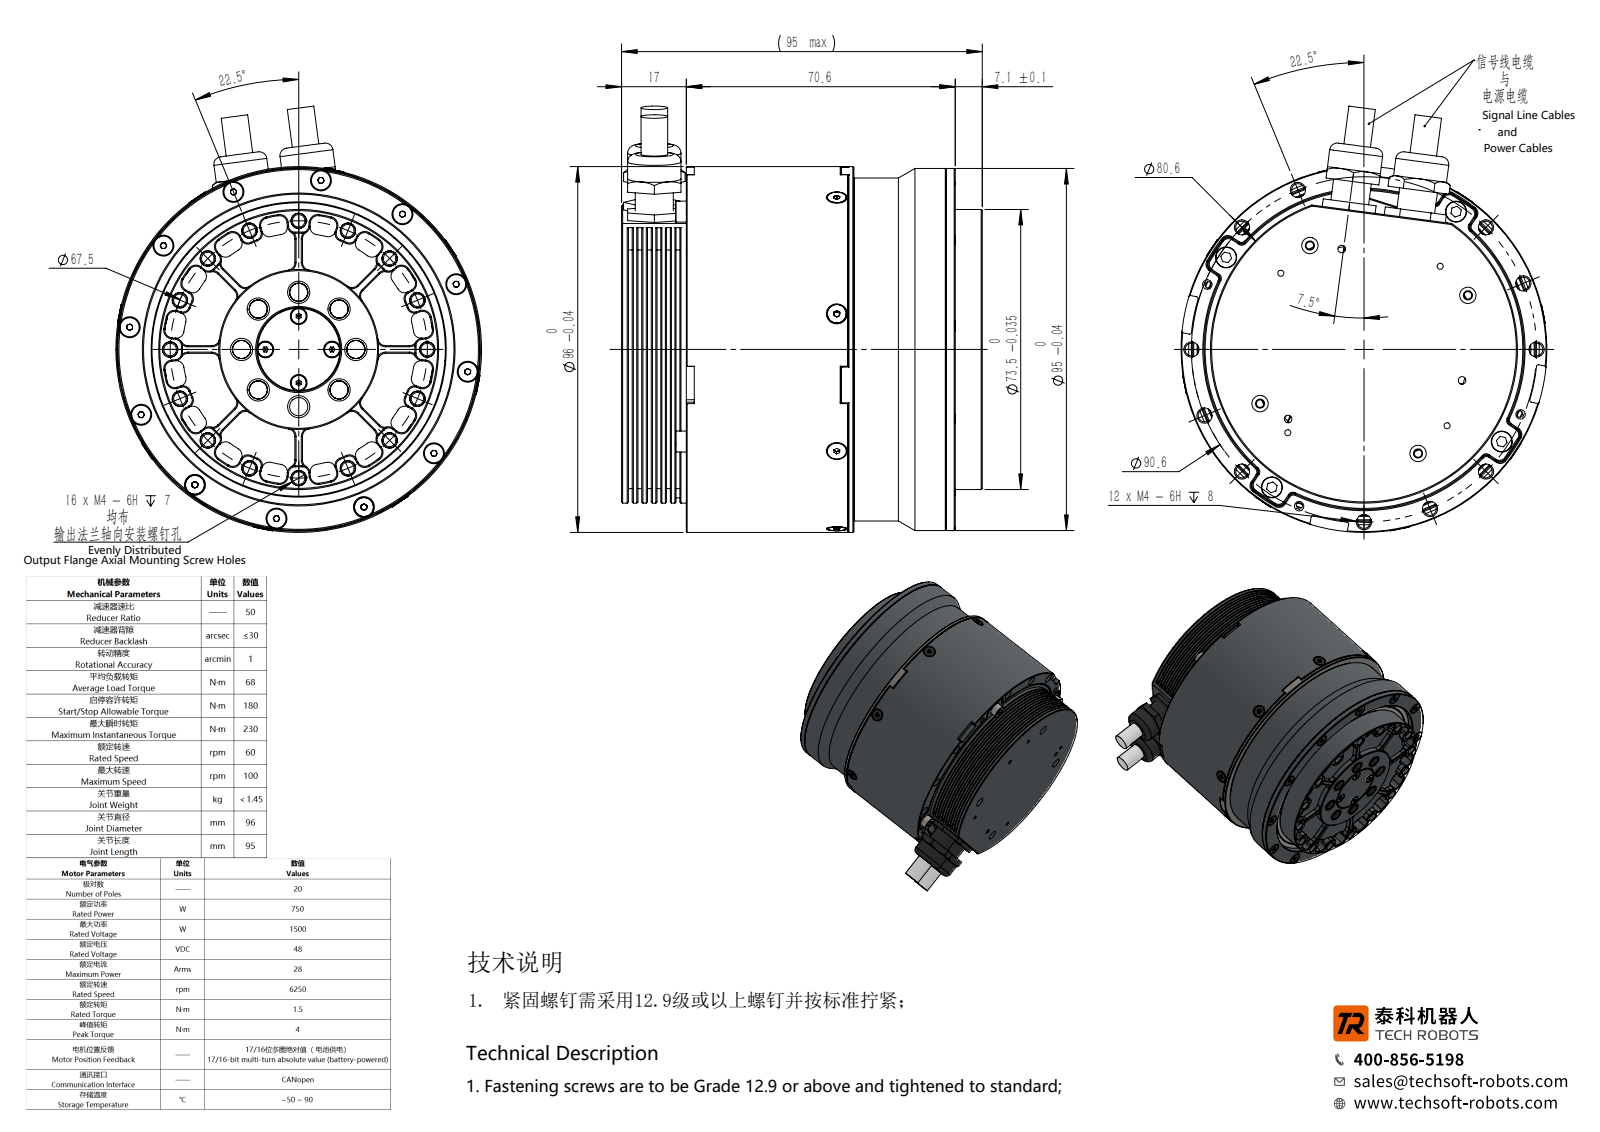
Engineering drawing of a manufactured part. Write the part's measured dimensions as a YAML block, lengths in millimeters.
step_written_by: "SolidWorks 2016 (CONFIG_CONTROL_DESIGN)"
units: millimeters
bodies: {solids: 8, faces: 1469, planar: 556, cylindrical: 443, other: 470}
overall_size: [111.86, 96, 94.7]
volume: 609441
surface_area: 54553
round_holes:
  - {diameter: 3.3, count: 28}
  - {diameter: 4, count: 28}
  - {diameter: 2.9, count: 20}
  - {diameter: 2, count: 4}
  - {diameter: 2.4, count: 4}
  - {diameter: 2.5, count: 3}
  - {diameter: 6.2, count: 2}
  - {diameter: 14, count: 1}
  - {diameter: 22, count: 1}
  - {diameter: 41.4, count: 1}
  - {diameter: 81.5, count: 1}
  - {diameter: 92, count: 1}
round_bosses_or_shafts:
  - {diameter: 5, count: 20}
  - {diameter: 2.5, count: 20}
  - {diameter: 5.5, count: 4}
  - {diameter: 14, count: 2}
  - {diameter: 10, count: 2}
  - {diameter: 7, count: 2}
  - {diameter: 96, count: 1}
  - {diameter: 95, count: 1}
partial_cylinders:
  - {radius: 1.02, count: 12}
  - {radius: 1.5, count: 8}
  - {radius: 2, count: 8}
  - {radius: 1.25, count: 1}
  - {radius: 31.85, count: 1}
  - {radius: 44.9, count: 1}
  - {radius: 45.5, count: 1}
  - {radius: 46.3, count: 1}
face_to_face_distances: [94.69, 9.59, 85.1, 7.09, 2.5, 87.6, 6.99, 2, 17, 77.69]
hole_center_spacings: [77.56, 19.14, 37.5, 56.49, 66.2, 66.04, 73.16, 33.75]
